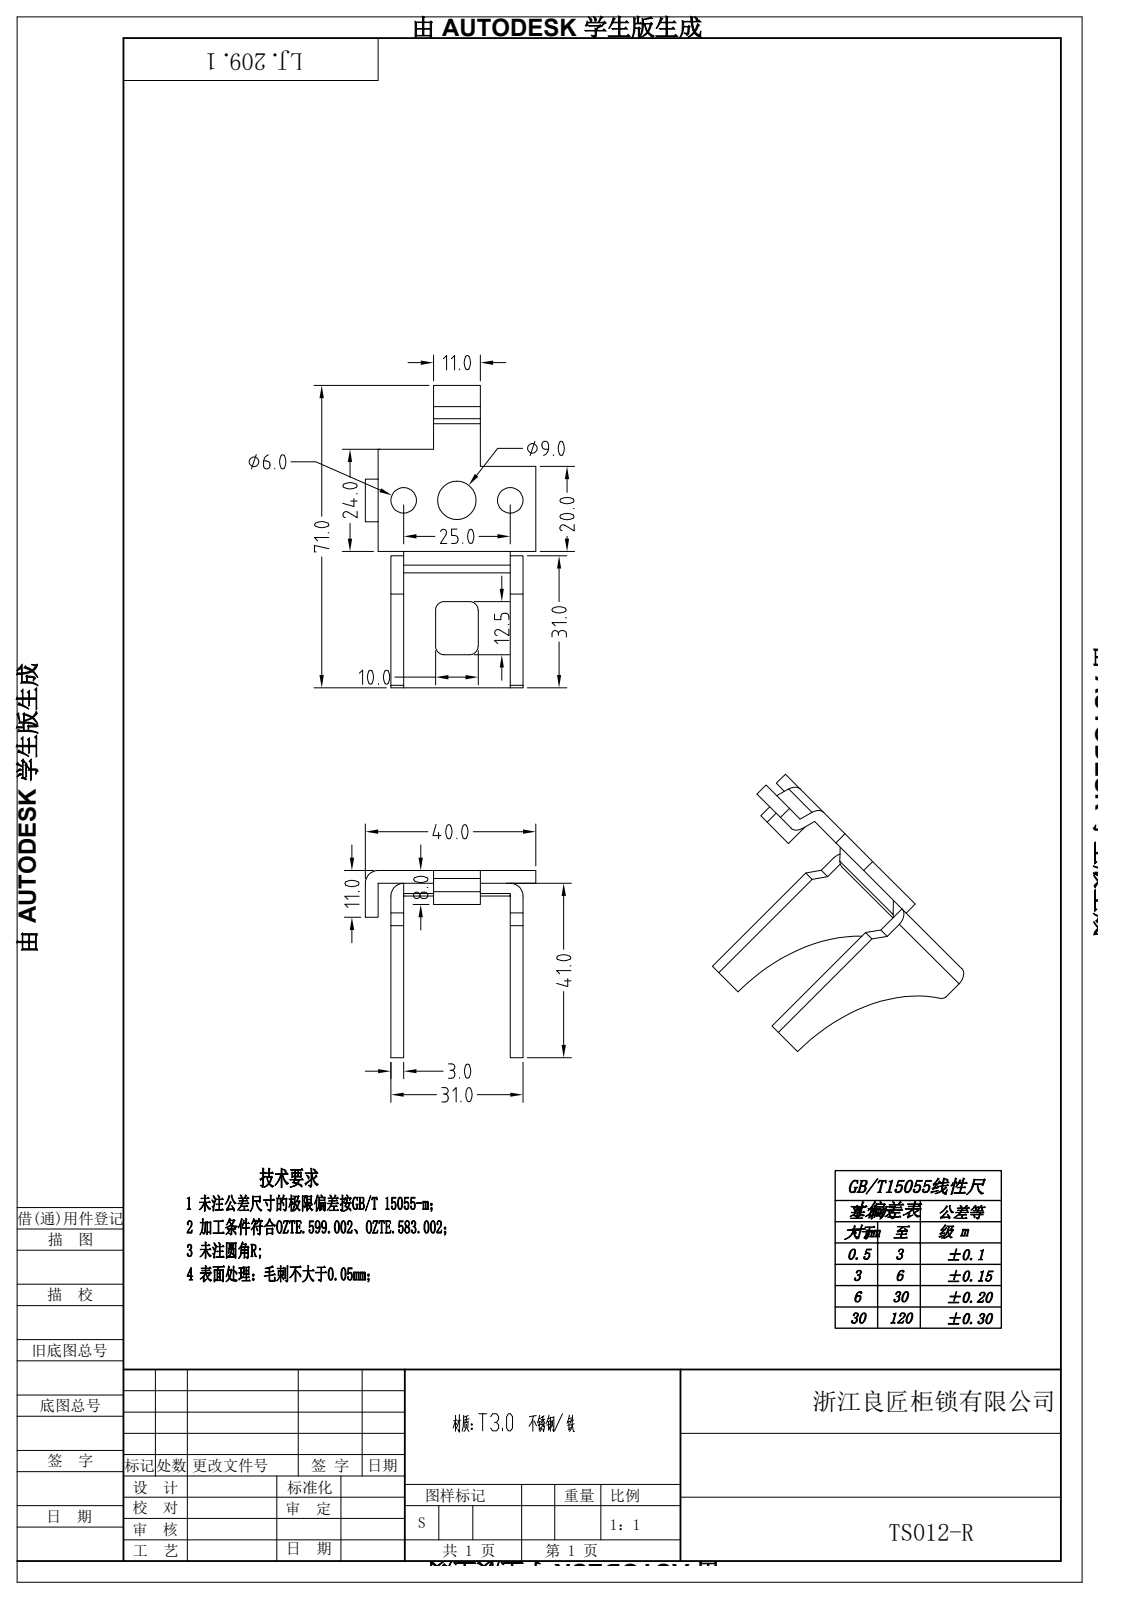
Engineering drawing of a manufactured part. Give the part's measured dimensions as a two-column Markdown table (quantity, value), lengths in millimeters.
| quantity | value |
| --- | --- |
| STEP written by | Rhino 8.5 (CONFIG_CONTROL_DESIGN) |
| units | millimeters |
| bodies | 4 solids, 194 faces (115 planar, 74 cylindrical, 5 other) |
| overall size | 139.65 × 97.29 × 47.5 |
| volume | 20 938 mm³ |
| surface area | 17 146 mm² |
| round holes (diameter × count) | 6 × 4, 9 × 2 |
| partial cylindrical surfaces (radius × count) | 3 × 10, 1.5 × 8, 2 × 8, 1 × 6, 0.5 × 3, 36.15 × 1 |
| main face-to-face distances | 3, 96.65, 28, 31, 6, 99.65, 93.65, 68.65, 124.65, 25 |
| hole center spacings | 12.5, 96.65, 25, 84.15, 109.15, 71.65, 121.65 |
